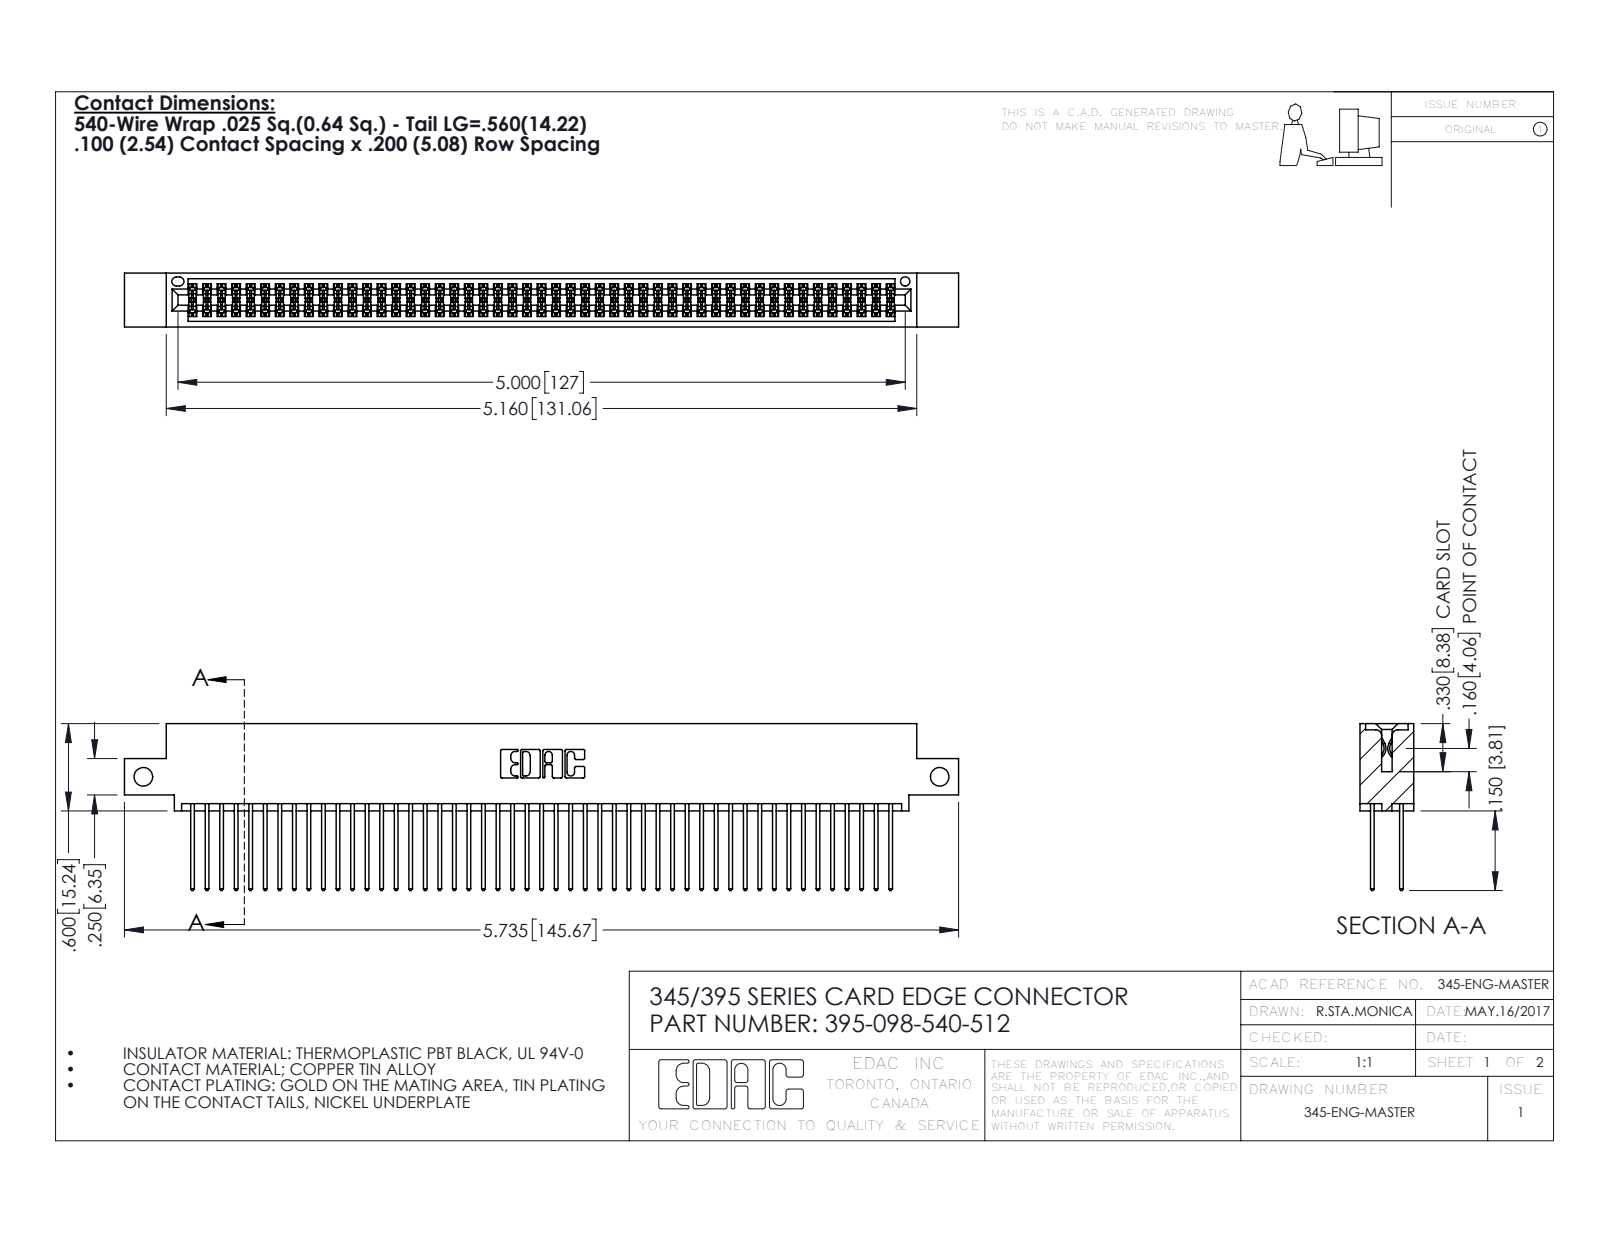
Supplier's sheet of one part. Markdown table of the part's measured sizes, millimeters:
| quantity | value |
| --- | --- |
| part name | 345-292-001_345-293-140; 395-098-540-512; 345 Part_0.110 Offset - Side Mount |
| STEP written by | SolidWorks 2016 (CONFIG_CONTROL_DESIGN) |
| units | millimeters |
| bodies | 99 solids, 5030 faces (3318 planar, 1712 cylindrical, 0 other) |
| overall size | 145.7 × 29.1 × 9.4 |
| volume | 14 400 mm³ |
| surface area | 23 140 mm² |
| round holes (diameter × count) | 3.3 × 2, 1.6 × 1 |
| partial cylindrical surfaces (radius × count) | 0.2 × 147, 0.3 × 98, 0.3 × 22, 0.2 × 6, 0.8 × 6, 0.7 × 3, 0.4 × 2, 0.5 × 2 |
| main face-to-face distances | 1.8, 7.6, 5.1, 2.5, 6.9, 0.6, 9.4, 5.7, 4.4, 3.8 |
| hole center spacings | 139.1 |
